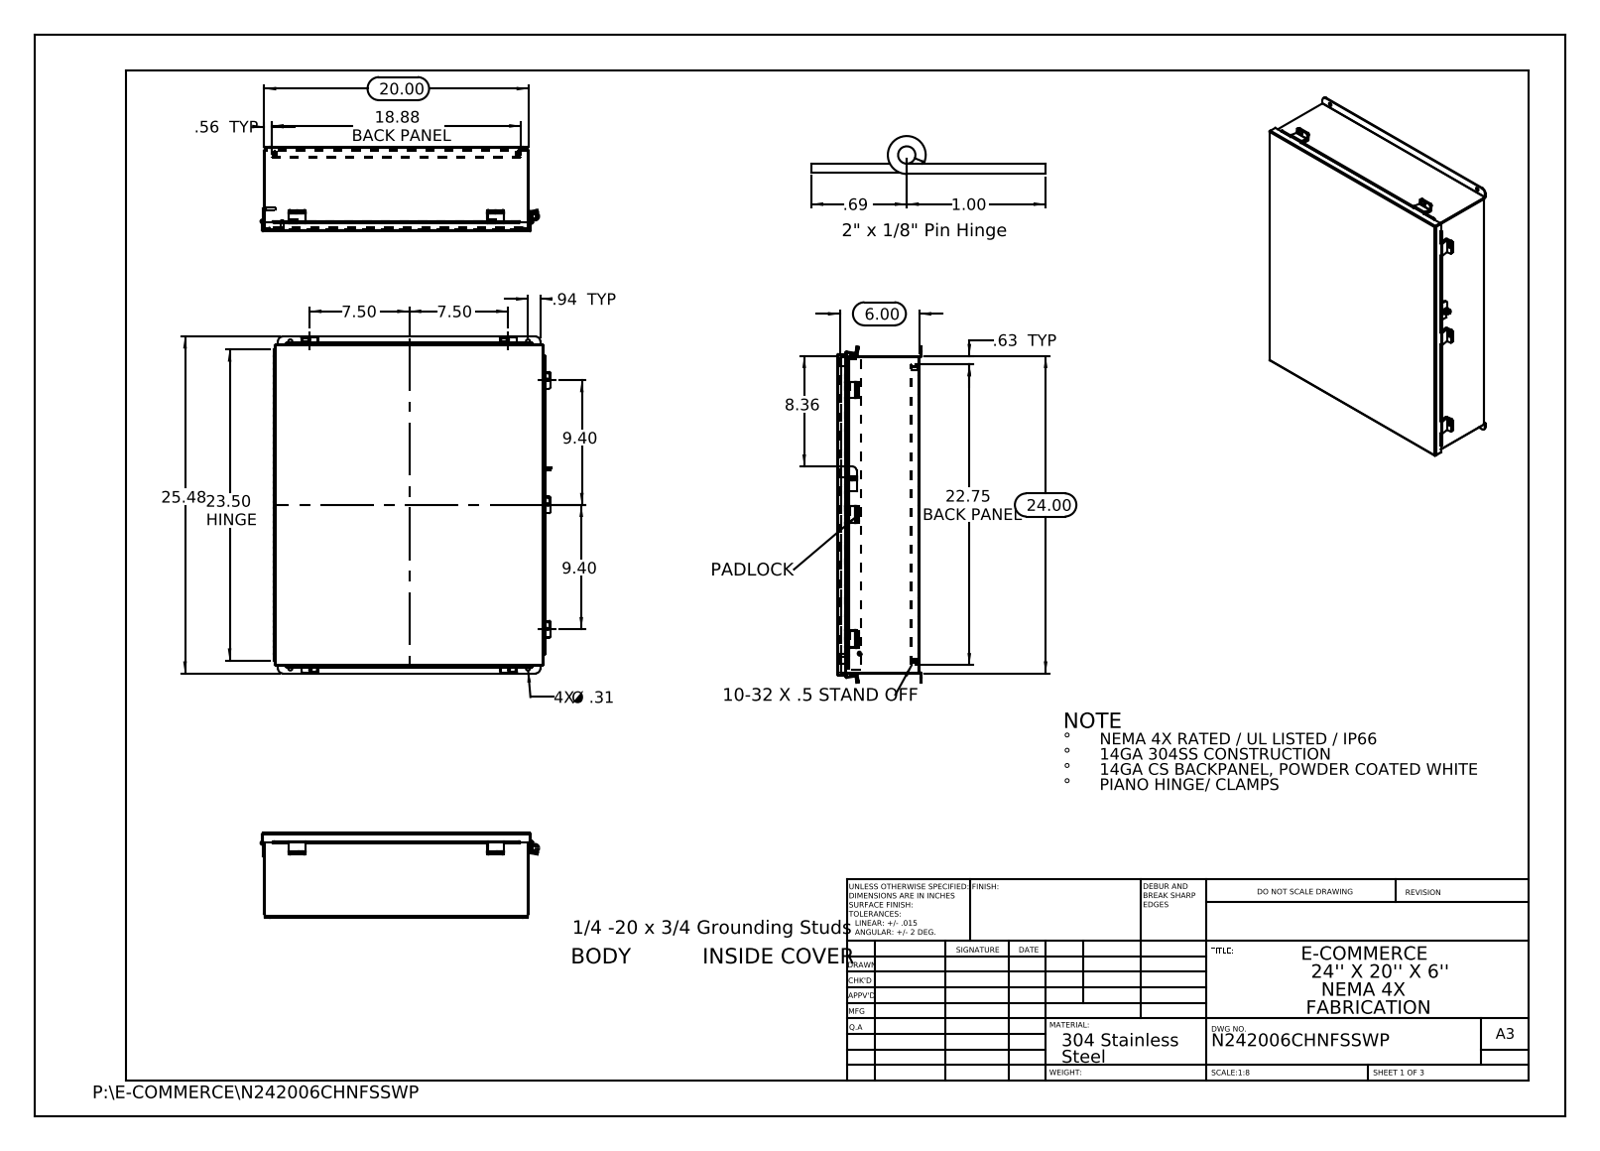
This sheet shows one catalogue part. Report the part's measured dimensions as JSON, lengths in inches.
{"part_name": "HW-CLH-JH-20104; N242006CHNFSSWP HW-CD-S-25020-034; N242006CHNFSSWP JIC Bottom; N242006CHNFSSWP JIC Top (+8 more)", "step_written_by": "SolidWorks 2013 (CONFIG_CONTROL_DESIGN)", "units": "inches", "bodies": {"solids": 29, "faces": 1012, "planar": 651, "cylindrical": 341, "other": 20}, "overall_size": [25.476, 21.072, 6.39], "volume_in3": 157.9, "surface_area_in2": 4279, "round_holes": [[0.25, 11], [0.187, 4], [0.312, 4], [0.125, 1], [0.125, 1], [0.373, 1], [0.375, 1]], "round_bosses_or_shafts": [[0.313, 4], [0.315, 2], [0.236, 2], [0.273, 1], [0.25, 1]], "partial_cylinders_radius": [[0.125, 24], [0.133, 14], [0.013, 13], [0.009, 12], [0.088, 12], [0.083, 6], [0.1, 6], [0.375, 4]], "face_to_face_distances": [0.075, 6.128, 6.053, 6.203, 0.074, 5.628, 0.575, 0.5, 5.553, 0.649], "hole_center_spacings": [1.315, 18.222, 23.427, 29.65, 9.425, 15, 17.976, 18.375]}
